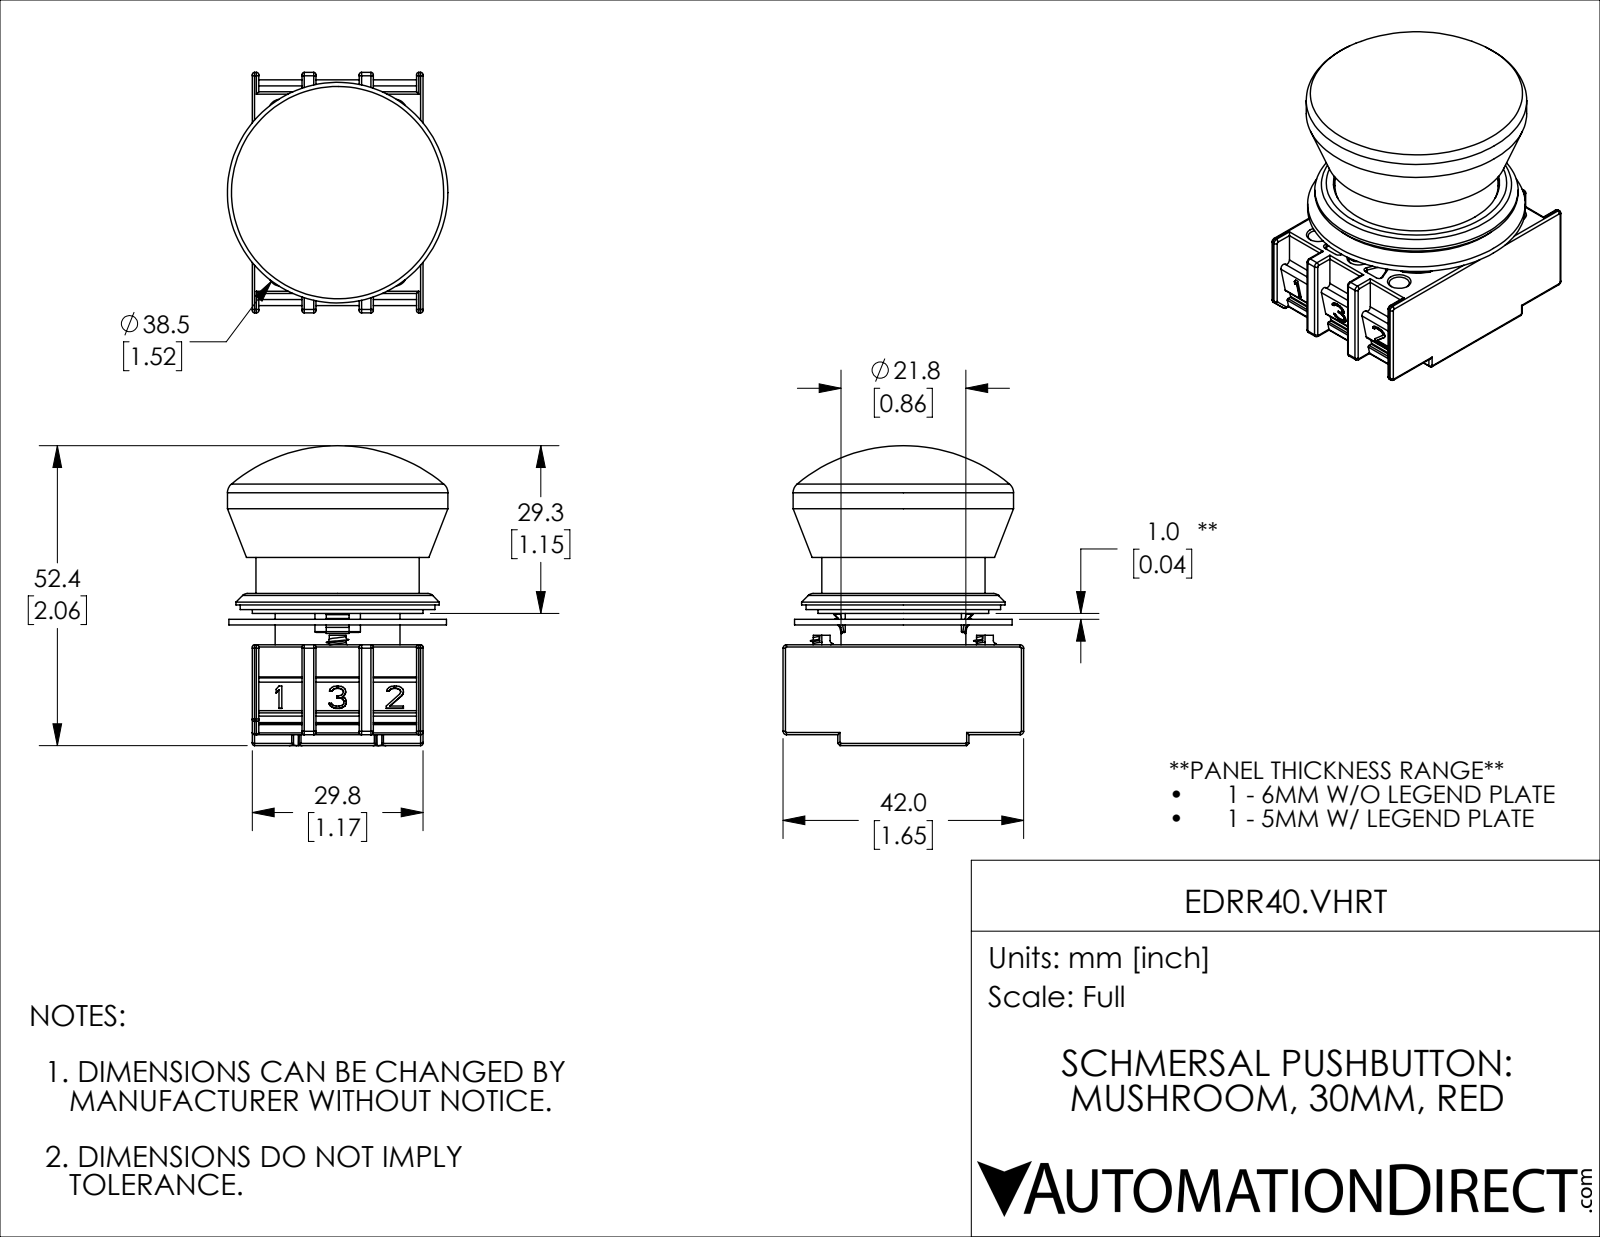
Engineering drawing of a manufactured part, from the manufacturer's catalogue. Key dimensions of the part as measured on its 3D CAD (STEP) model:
Part name (STEP PRODUCT): EDRR40.VHRT
STEP written by: SolidWorks 2019 (CONFIG_CONTROL_DESIGN)
Units: millimetres
Bodies: 8 solids, 1427 faces (532 planar, 486 cylindrical, 409 other)
Overall size (bounding box): 52.2 × 42 × 38.5
Volume: 31 122 mm³ · Surface area: 21 472 mm²
Round holes (diameter × count): ⌀3.5 ×6, ⌀5.15 ×6, ⌀3.1 ×1, ⌀5.8 ×1, ⌀13.8 ×1, ⌀22.2 ×1, ⌀22.3 ×1, ⌀22.5 ×1, ⌀28.5 ×1, ⌀29 ×1, ⌀30 ×1
Round bosses / shafts (diameter × count): ⌀4.8 ×2, ⌀2.93 ×2, ⌀38.5 ×1, ⌀38 ×1, ⌀35.5 ×1, ⌀34 ×1, ⌀29.8 ×1, ⌀27.8 ×1
Partial cylindrical surfaces — rounded edges, fillets, slot ends (radius × count): R0.4 ×112, R0.3 ×48, R0.2 ×24, R0.6 ×8, R0.5 ×6, R0.8 ×6, R0.1 ×2, R0.12 ×2
Main face-to-face distances: 1, 29.8, 13.2, 12.2, 4.45, 21.05, 22.05, 34.25, 1.5, 16.65
Hole centre spacings: 10, 17.41, 30.2, 28.5, 14.25, 20, 34.82
